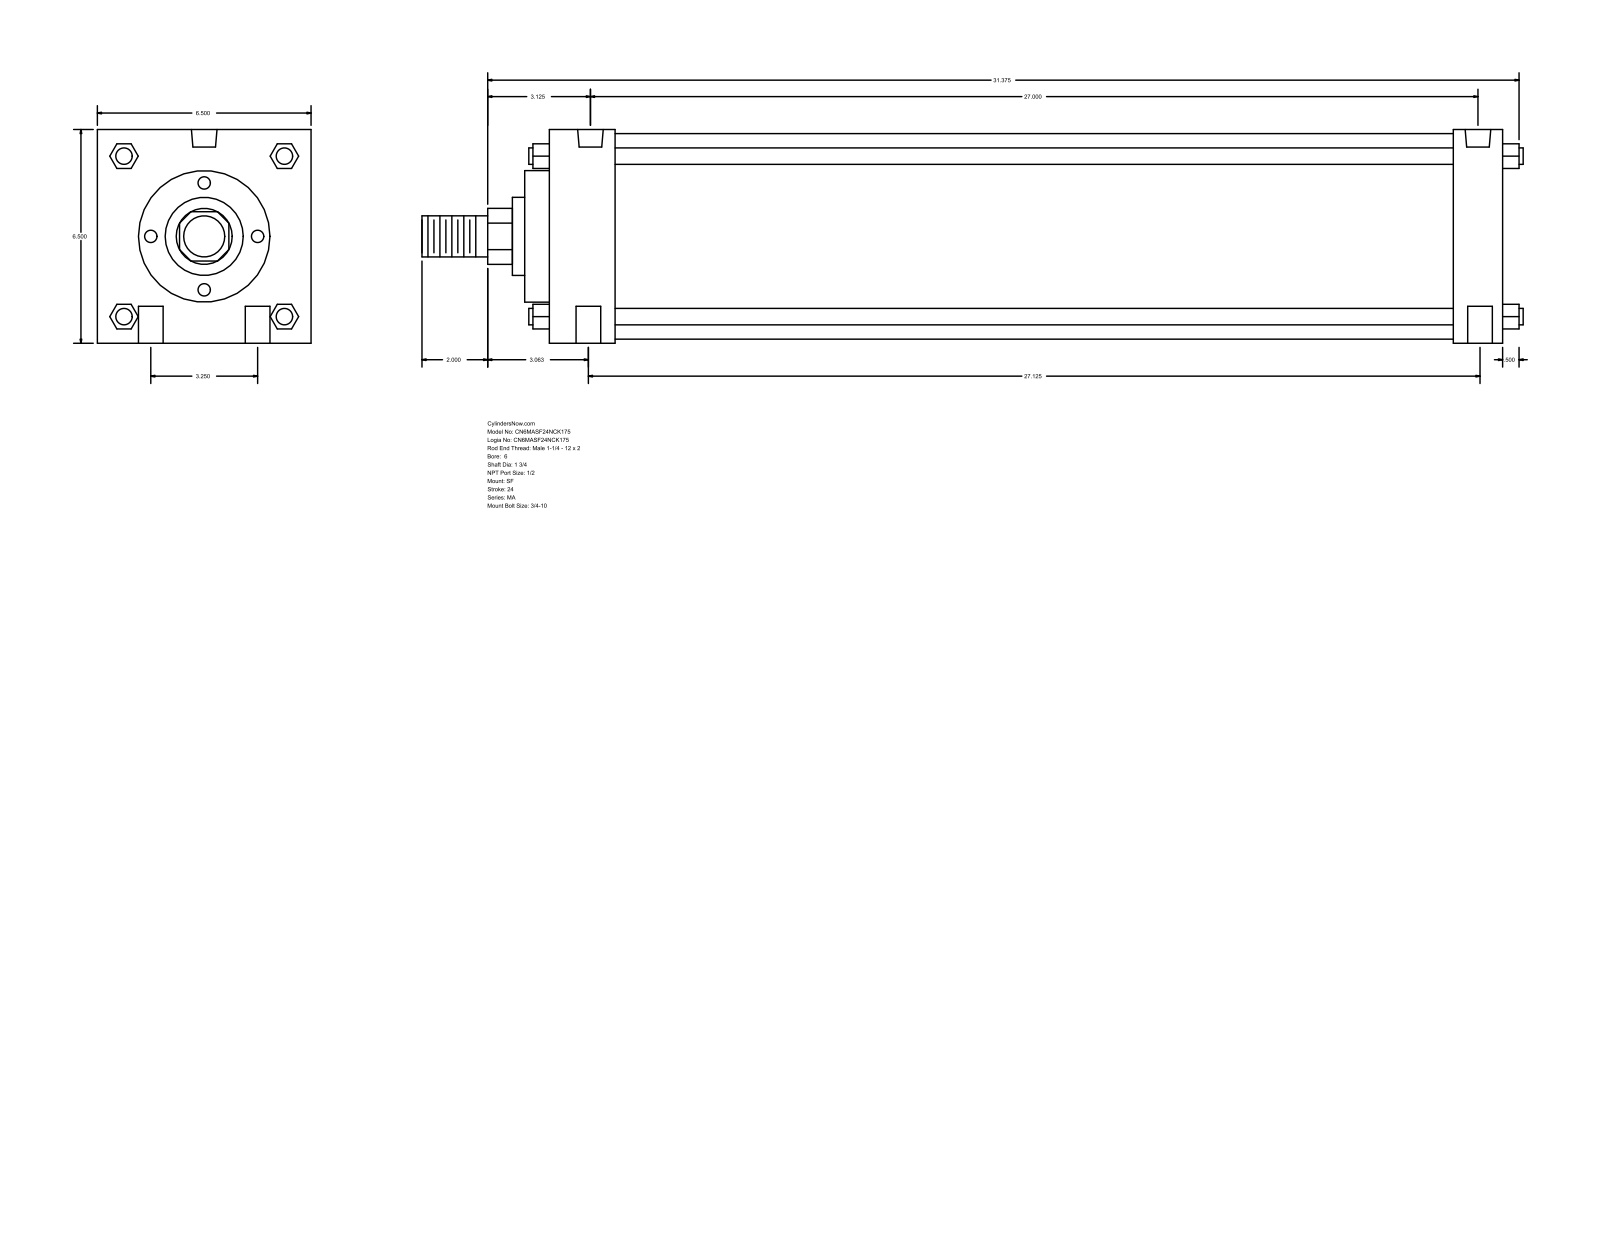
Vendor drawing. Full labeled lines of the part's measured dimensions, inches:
Part name (STEP PRODUCT): MA_SF__0600_1.75
STEP written by: GSSL Pune (CONFIG_CONTROL_DESIGN)
Units: inches
Bodies: 0 solids, 126 faces (95 planar, 31 cylindrical, 0 other)
Overall size (bounding box): 33.5 × 6.5 × 6.5
Round holes (diameter × count): ⌀0.75 ×4, ⌀0.687 ×2, ⌀0.778 ×2
Round bosses / shafts (diameter × count): ⌀0.5 ×4, ⌀6.25 ×1, ⌀4 ×1, ⌀2.375 ×1, ⌀1.75 ×1, ⌀1.25 ×1
Partial cylindrical surfaces — rounded edges, fillets, slot ends (radius × count): R0.852 ×1
Main face-to-face distances: 6.5, 29, 0.75, 2, 27.5, 1.5, 25.5, 27, 2.75, 28.25
Hole centre spacings: 1.626, 27.111, 3.25, 27, 27.125, 27.319
